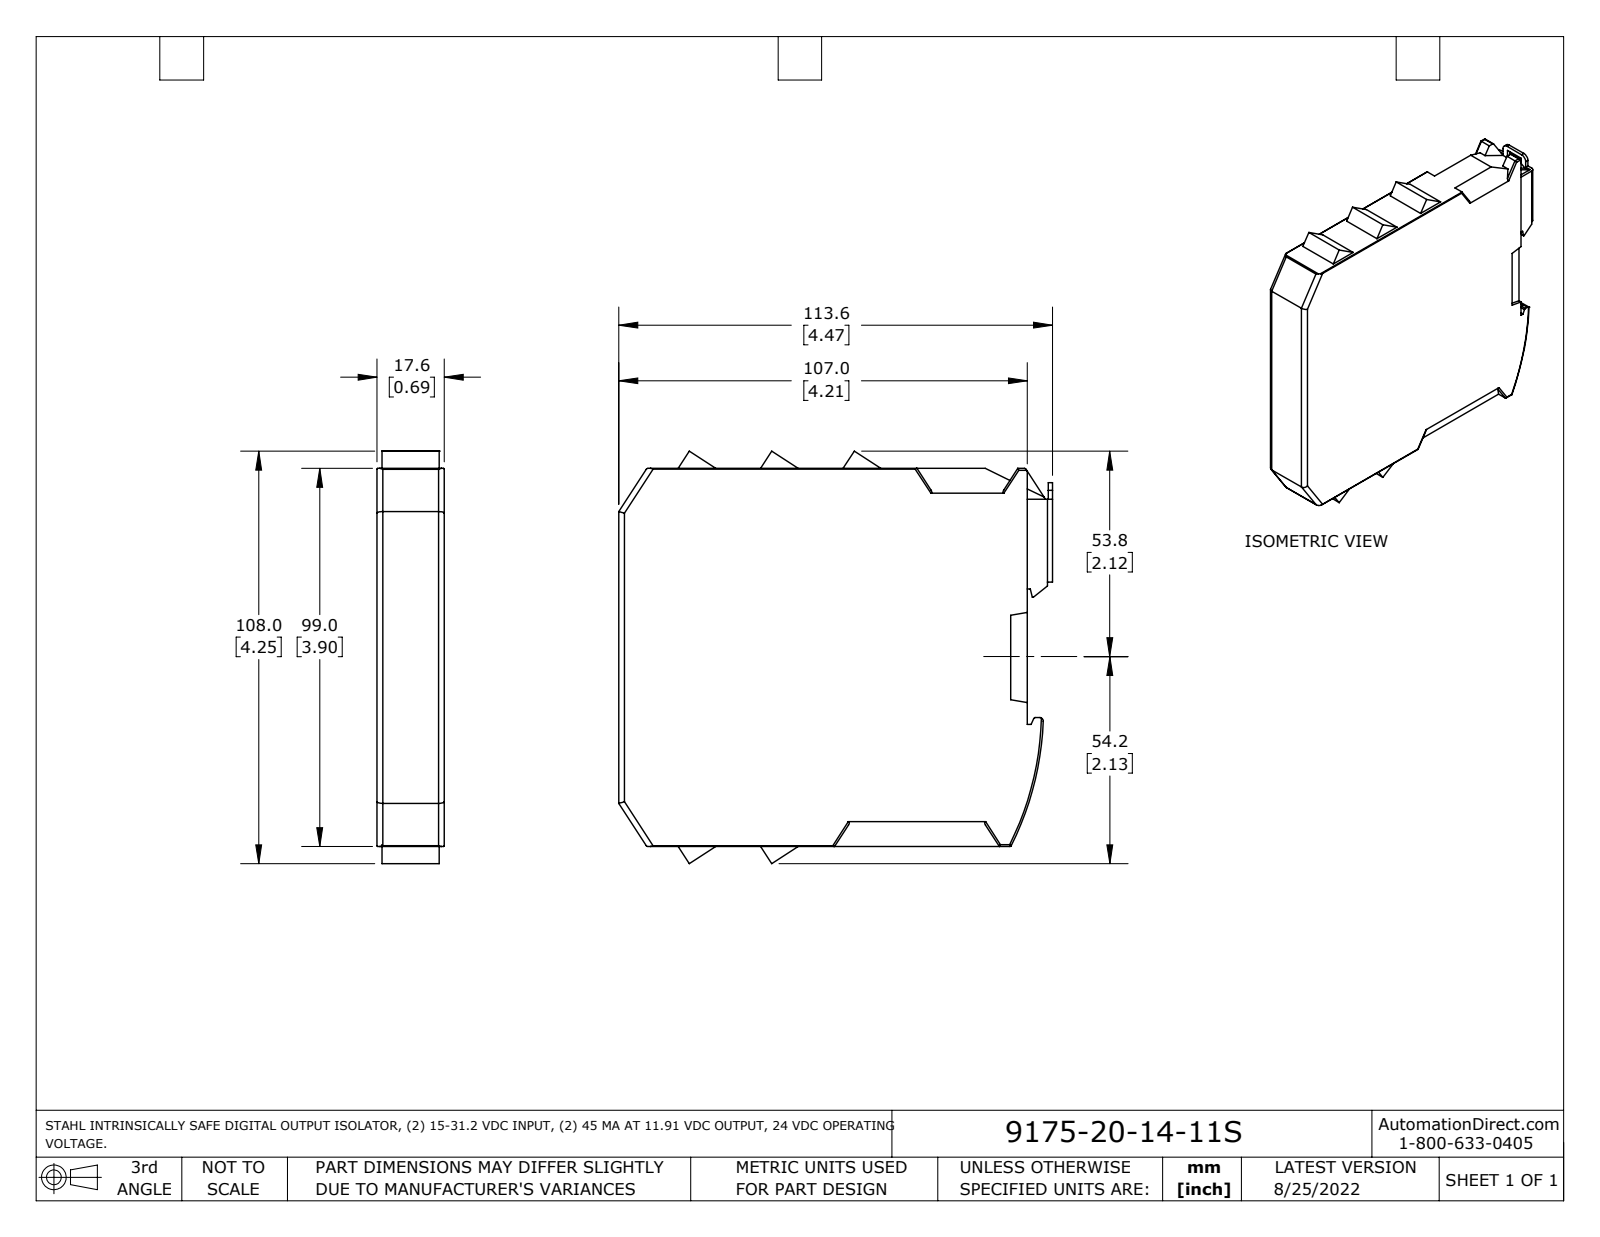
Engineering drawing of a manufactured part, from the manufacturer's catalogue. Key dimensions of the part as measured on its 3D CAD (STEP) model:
Part name (STEP PRODUCT): 9175-20-14-11S
STEP written by: SolidWorks 2021 (AUTOMOTIVE_DESIGN)
Units: inches
Bodies: 2 solids, 181 faces (127 planar, 52 cylindrical, 2 other)
Overall size (bounding box): 4.472 × 4.252 × 0.693
Volume: 11.44 in³ · Surface area: 46.75 in²
Partial cylindrical surfaces — rounded edges, fillets, slot ends (radius × count): R0.02 ×17, R0.059 ×6, R0.008 ×4, R0.028 ×4, R0.051 ×2, R0.079 ×2, R0.039 ×1, R3.15 ×1
Main face-to-face distances: 0.693, 3.898, 4.213, 0.041, 0.652, 0.217, 4.429, 0.043, 0.26, 4.472
